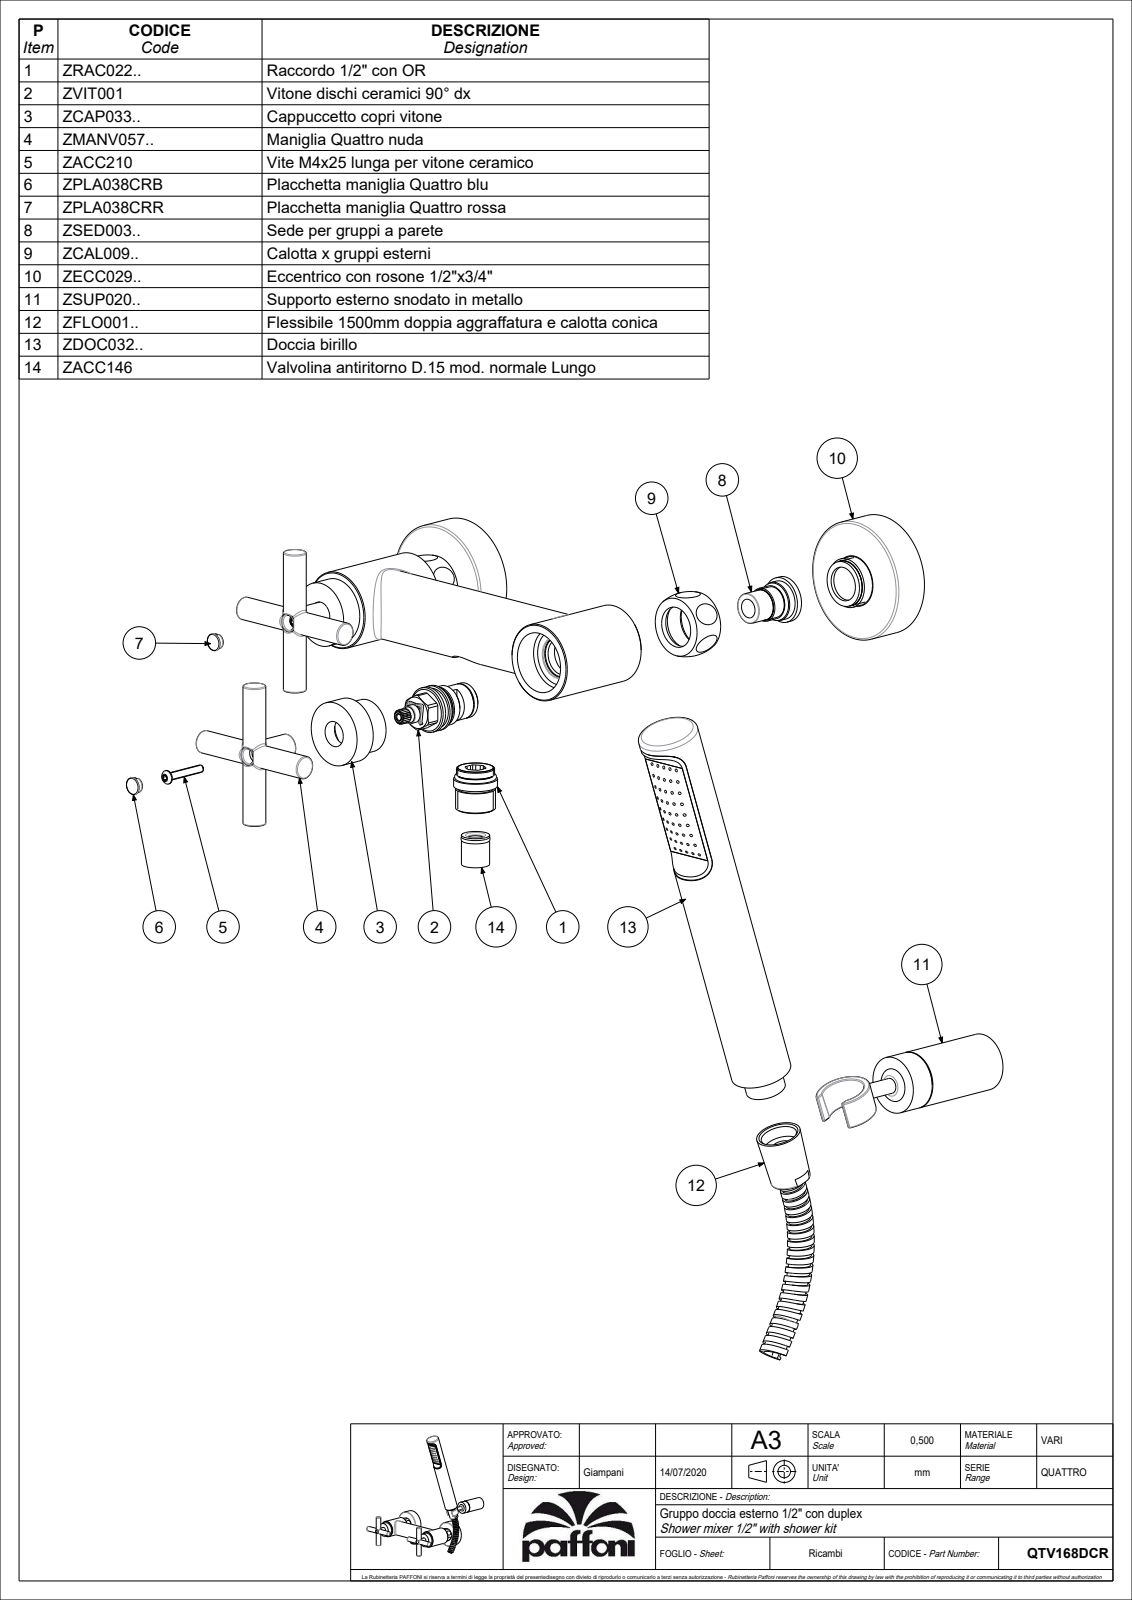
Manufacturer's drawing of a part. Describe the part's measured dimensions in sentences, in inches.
The part is named "QTV168DCR". Its 3-D file was written by "CREO PARAMETRIC BY PTC INC, 2020044 (CONFIG_CONTROL_DESIGN)". It is 5 solids with 1039 faces: 434 planar, 326 cylindrical and 279 other. Overall it measures 13.746 by 11.949 by 7.47 inches. Its volume is 28.37 cubic inches and its surface area 249.1 square inches. Round holes: 45 of diameter 0.059, 2 of diameter 0.13, 2 of diameter 0.177, 2 of diameter 0.276, 2 of diameter 0.315, 2 of diameter 0.346, 2 of diameter 0.374, 2 of diameter 0.394, 2 of diameter 0.531, 2 of diameter 0.709, 2 of diameter 0.846, 2 of diameter 0.906. Round bosses or shafts: 3 of diameter 0.472, 2 of diameter 2.5, 2 of diameter 1.614, 2 of diameter 1.339, 2 of diameter 1.063, 2 of diameter 0.945, 2 of diameter 0.807, 2 of diameter 0.512. Partial cylindrical surfaces (rounded edges, fillets, slot ends): 34 of radius 0.004, 14 of radius 0.02, 4 of radius 0.039, 2 of radius 0.118, 2 of radius 0.307, 2 of radius 0.37, 2 of radius 0.386, 2 of radius 0.394. The main face-to-face distances are 0.024, 2.669, 0.752, 0.728, 3.421, 3.398, 0.079, 2.709, 0.039, 0.787. The hole center spacings are 0.311, 0.256, 0.542, 0.177, 0.437, 0.788, 0.512, 1.039.
